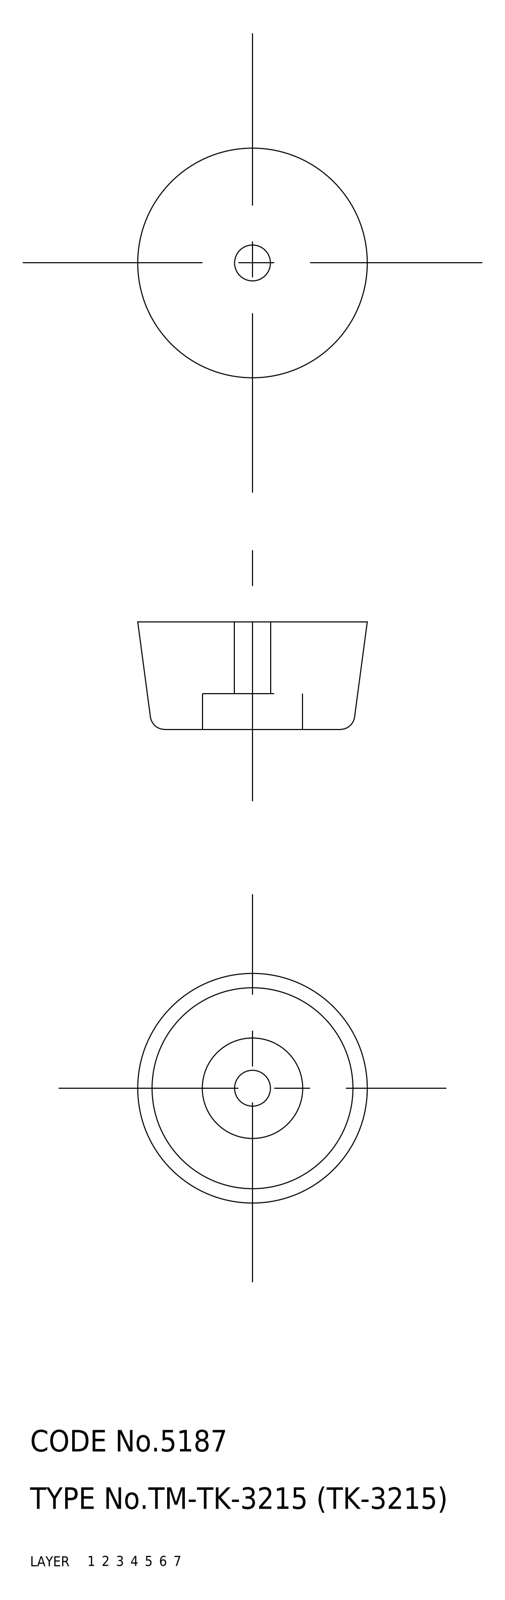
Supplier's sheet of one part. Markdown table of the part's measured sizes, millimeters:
| quantity | value |
| --- | --- |
| part name | washer; rubber foot; TK_3215_9670_36 |
| STEP written by | CADfix (AUTOMOTIVE_DESIGN) |
| units | millimeters |
| bodies | 2 solids, 20 faces (0 planar, 0 cylindrical, 20 other) |
| overall size | 32 × 32 × 15 |
| volume | 9 622 mm³ |
| surface area | 3 667 mm² |
